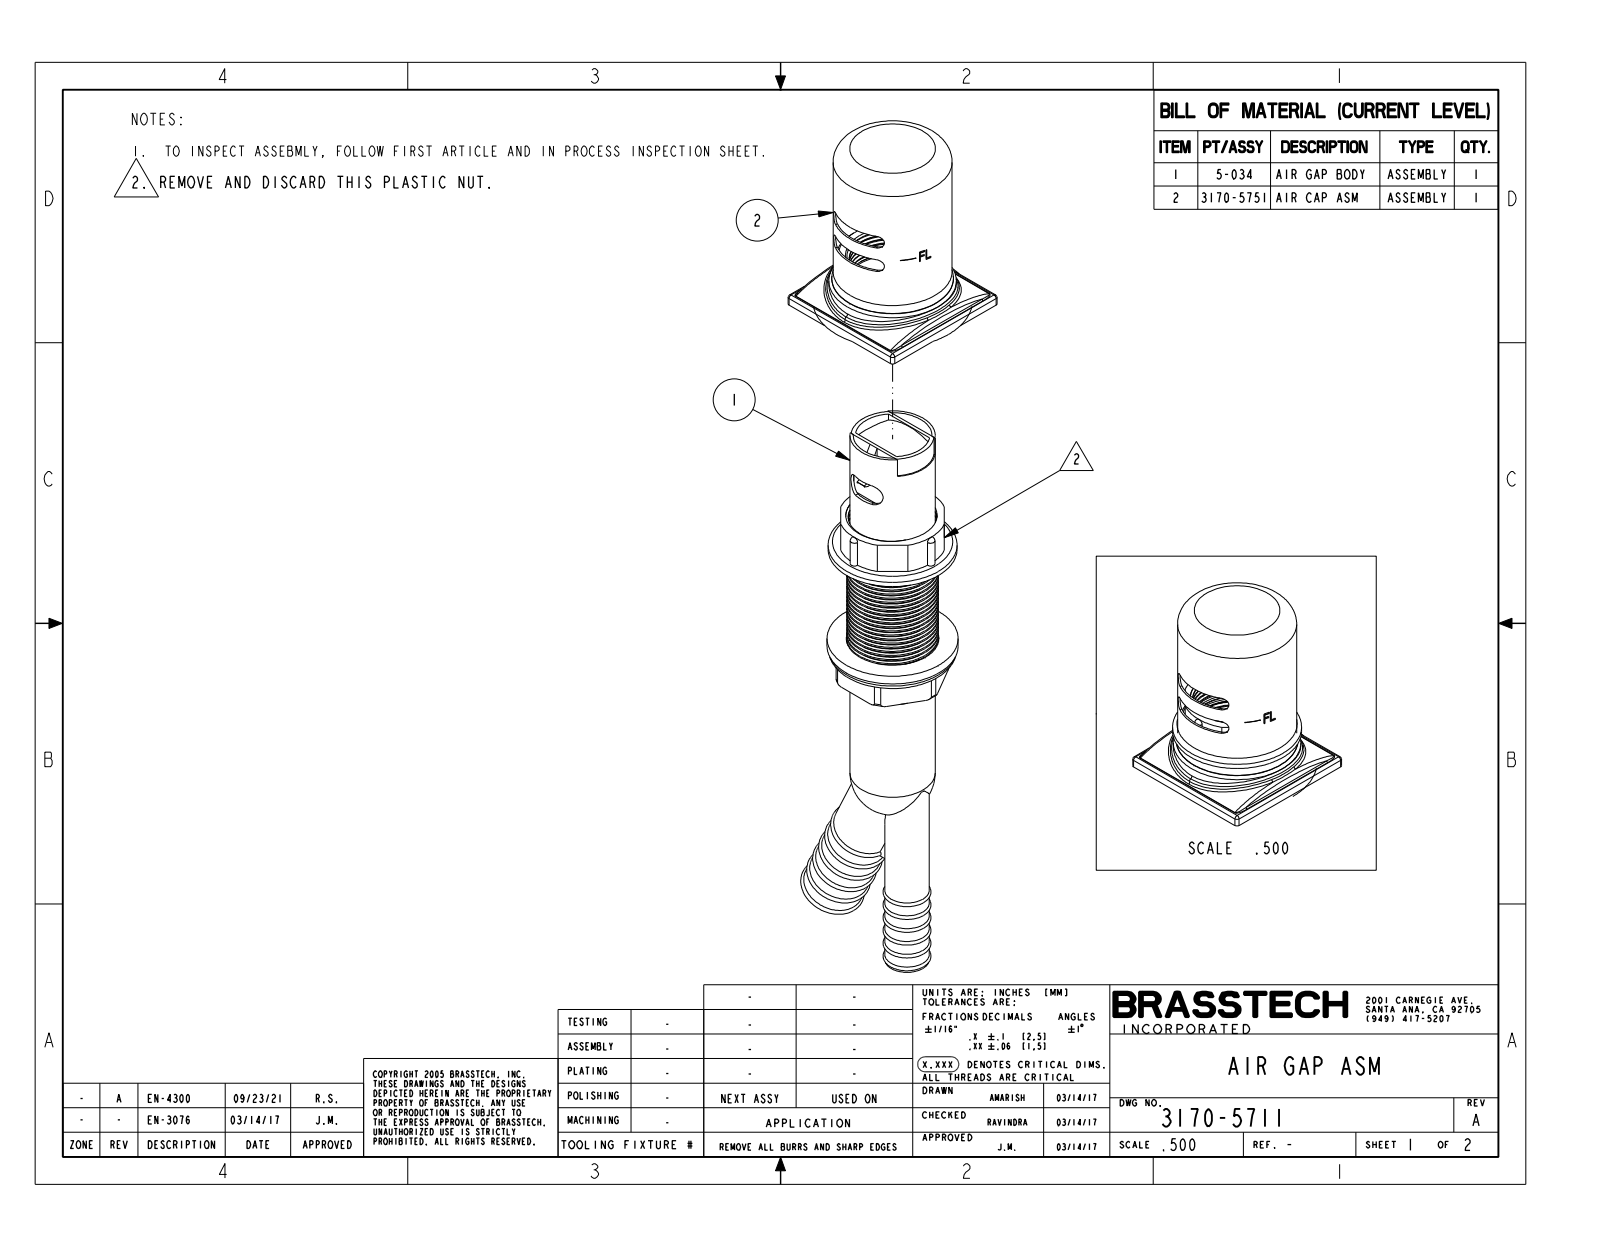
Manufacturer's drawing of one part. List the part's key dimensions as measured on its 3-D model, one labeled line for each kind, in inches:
Part name (STEP PRODUCT): 3170-5711
STEP written by: CREO PARAMETRIC BY PTC INC, 2018400 (AUTOMOTIVE_DESIGN)
Units: inches
Bodies: 2 solids, 310 faces (73 planar, 140 cylindrical, 97 other)
Overall size (bounding box): 8.803 × 2.607 × 2.05
Volume: 10.27 in³ · Surface area: 81.6 in²
Round holes (diameter × count): ⌀1.2 ×1, ⌀1.27 ×1, ⌀1.28 ×1, ⌀1.575 ×1
Round bosses / shafts (diameter × count): ⌀1.8 ×1, ⌀1.76 ×1, ⌀1.75 ×1, ⌀1.635 ×1, ⌀1.259 ×1, ⌀1.17 ×1, ⌀0.854 ×1, ⌀0.61 ×1
Partial cylindrical surfaces — rounded edges, fillets, slot ends (radius × count): R0.04 ×14, R0.02 ×4, R0.098 ×4, R0.157 ×2, R0.808 ×1
Main face-to-face distances: 0.92, 3.505, 3.535, 2.585, 2.615, 0.03, 1.345, 0.425, 2.16, 2.19
